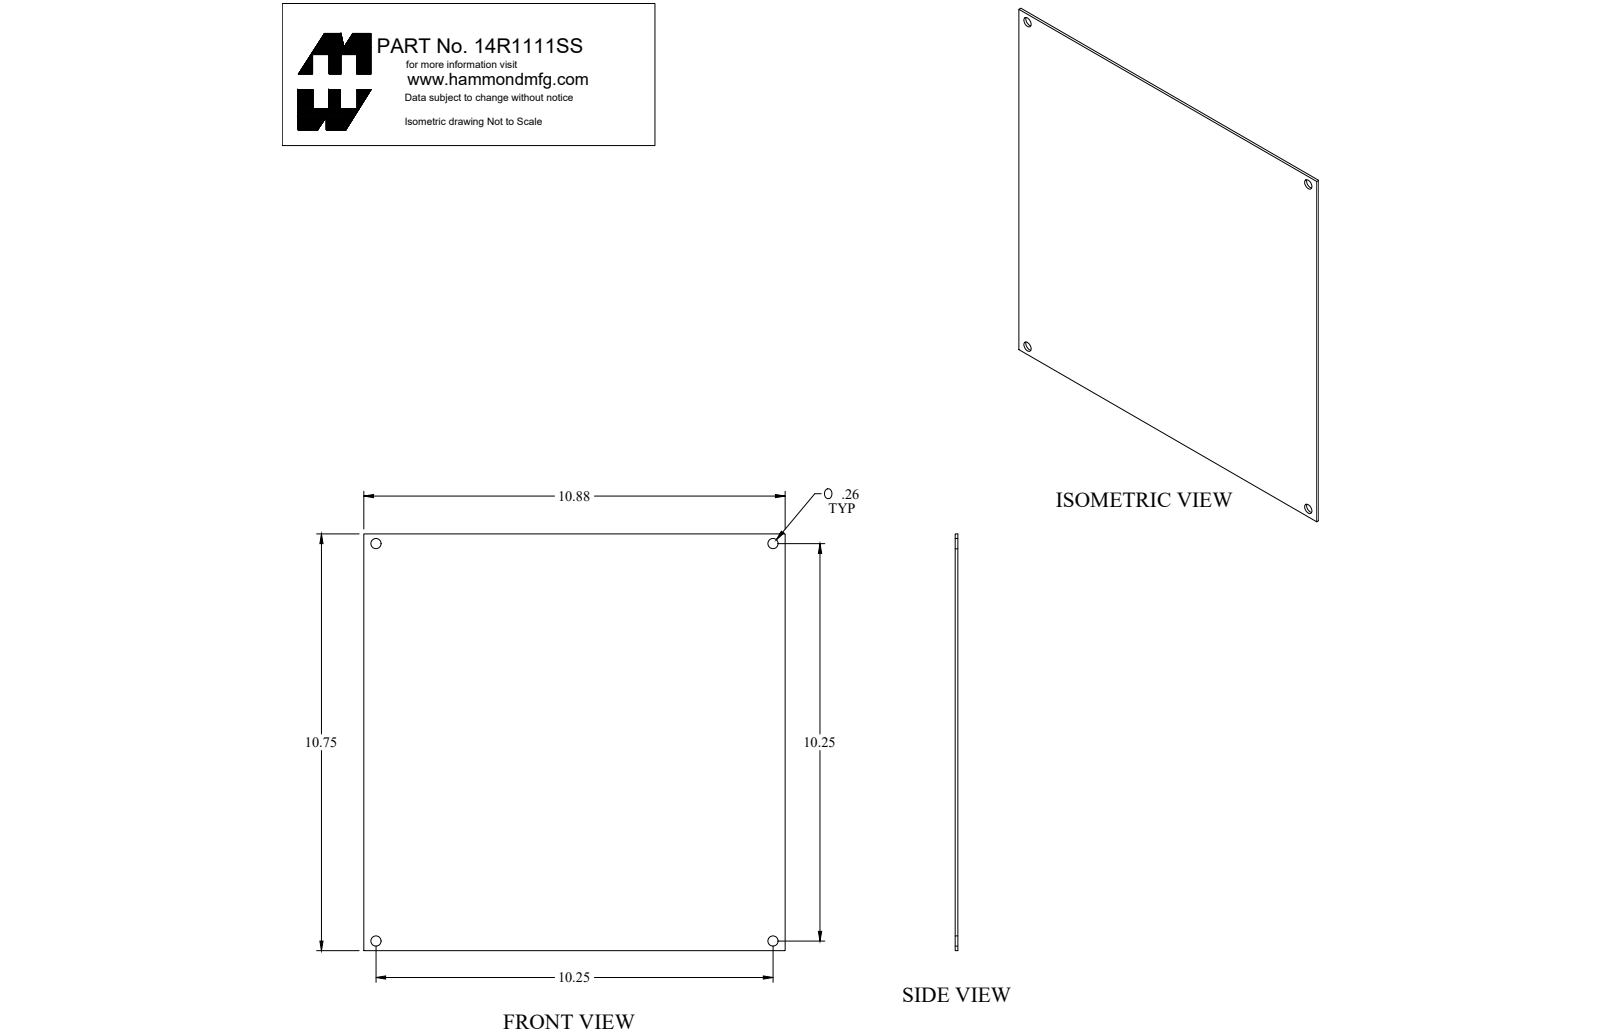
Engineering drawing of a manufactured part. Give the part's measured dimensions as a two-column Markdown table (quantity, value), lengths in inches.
| quantity | value |
| --- | --- |
| part name | 14R1111SS |
| STEP written by | SolidWorks 2018 (AUTOMOTIVE_DESIGN) |
| units | inches |
| bodies | 1 solid, 10 faces (6 planar, 4 cylindrical, 0 other) |
| overall size | 10.875 × 10.75 × 0.072 |
| volume | 8.401 in³ |
| surface area | 236.7 in² |
| round holes (diameter × count) | 0.265 × 4 |
| main face-to-face distances | 0.072, 10.75, 10.875 |
| hole center spacings | 10.25, 14.496 |
